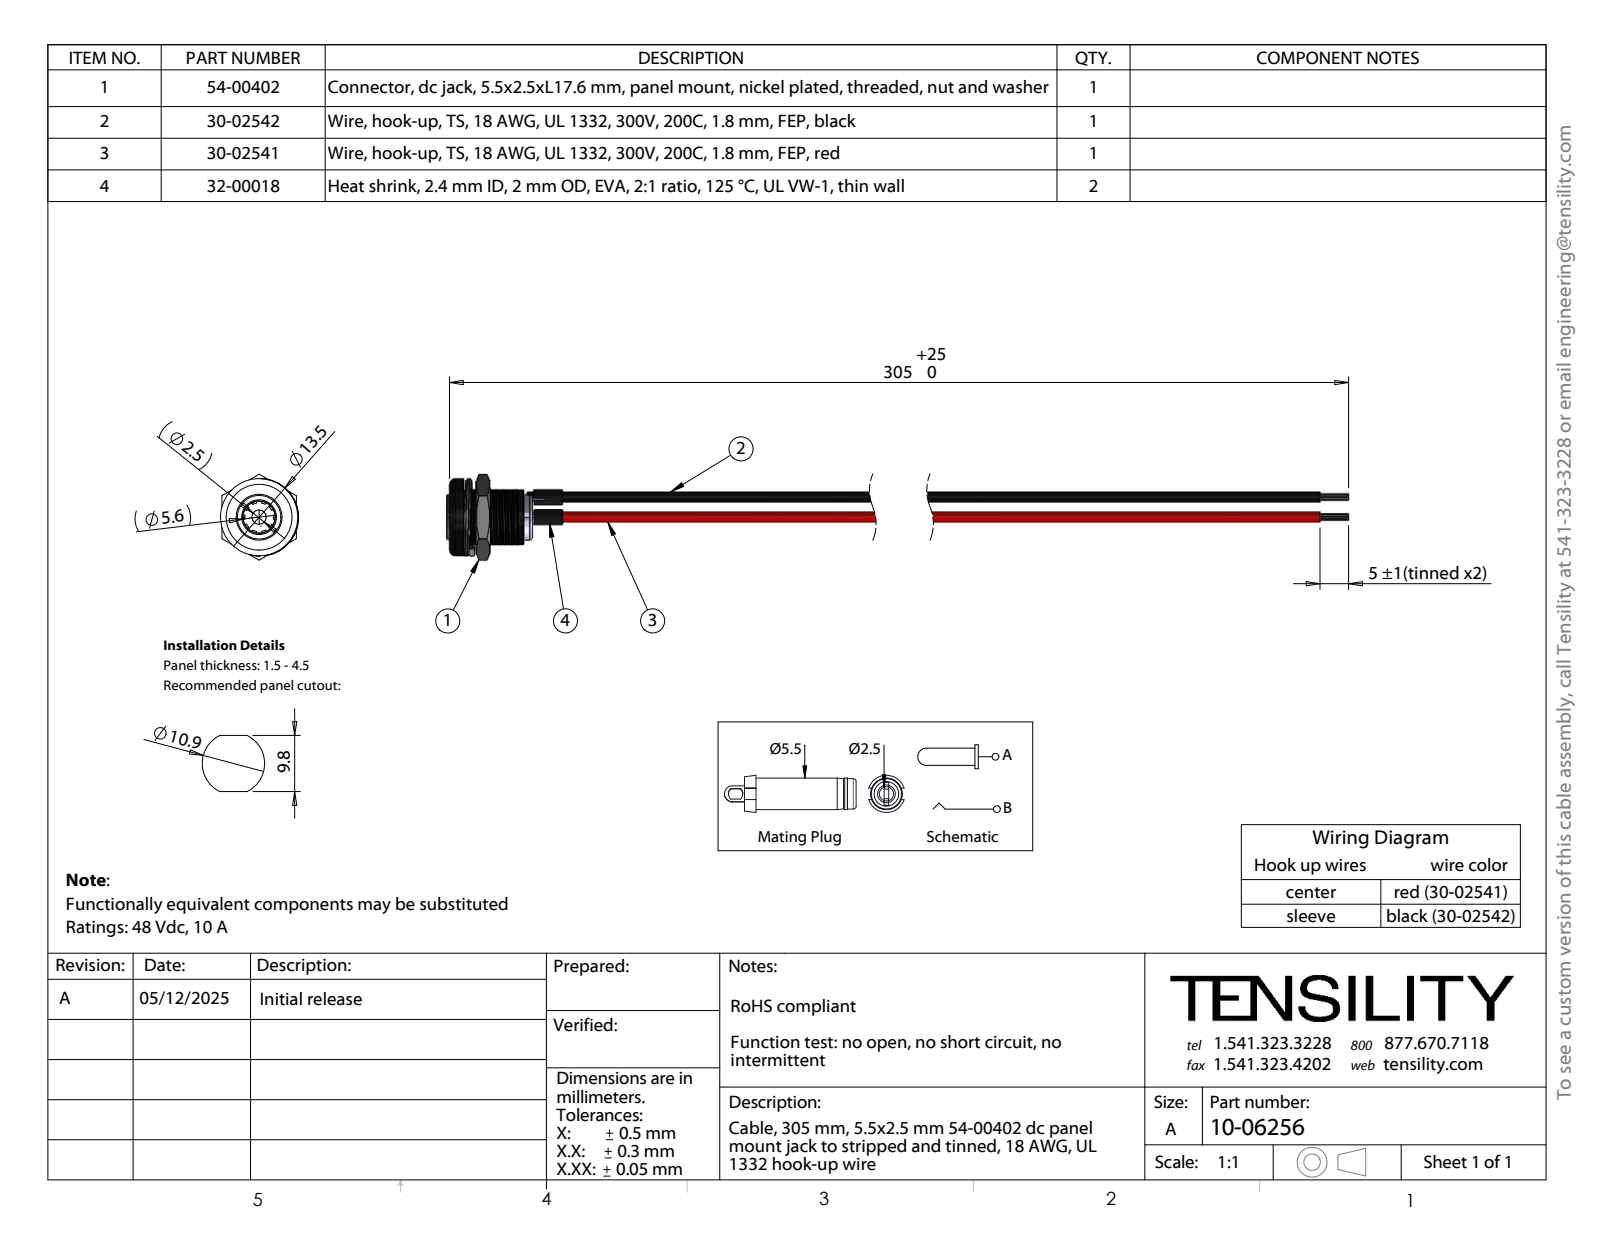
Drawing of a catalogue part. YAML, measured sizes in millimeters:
part_name: "50-01013 insulator_Insulator; 32-00018_round 10-06314; 56-00001_Helical - Render; 50-01013 spring contact_Terminal (+8 more)"
step_written_by: "SolidWorks 2021 (CONFIG_CONTROL_DESIGN)"
units: millimeters
bodies: {solids: 49, faces: 540, planar: 172, cylindrical: 241, other: 127}
overall_size: [169.02, 15.01, 13.64]
volume: 1997
surface_area: 13367
round_holes:
  - {diameter: 0.24, count: 38}
  - {diameter: 1.5, count: 2}
  - {diameter: 1.6, count: 1}
  - {diameter: 2.15, count: 1}
  - {diameter: 2.47, count: 1}
  - {diameter: 5.6, count: 1}
  - {diameter: 5.65, count: 1}
  - {diameter: 6.4, count: 1}
  - {diameter: 6.6, count: 1}
  - {diameter: 7.6, count: 1}
  - {diameter: 8, count: 1}
  - {diameter: 10.3, count: 1}
round_bosses_or_shafts:
  - {diameter: 1.8, count: 2}
  - {diameter: 13.5, count: 1}
  - {diameter: 9.6, count: 1}
  - {diameter: 7.3, count: 1}
  - {diameter: 6.2, count: 1}
partial_cylinders:
  - {radius: 0.5, count: 2}
  - {radius: 3.35, count: 1}
  - {radius: 5.4, count: 1}
face_to_face_distances: [2.5, 4.61, 13, 8.5, 11, 1, 7.11, 3.89, 2.11, 6.39]
hole_center_spacings: [0.65, 0.43, 0.49, 0.42, 0.85, 0.88, 0.89, 0.73]
